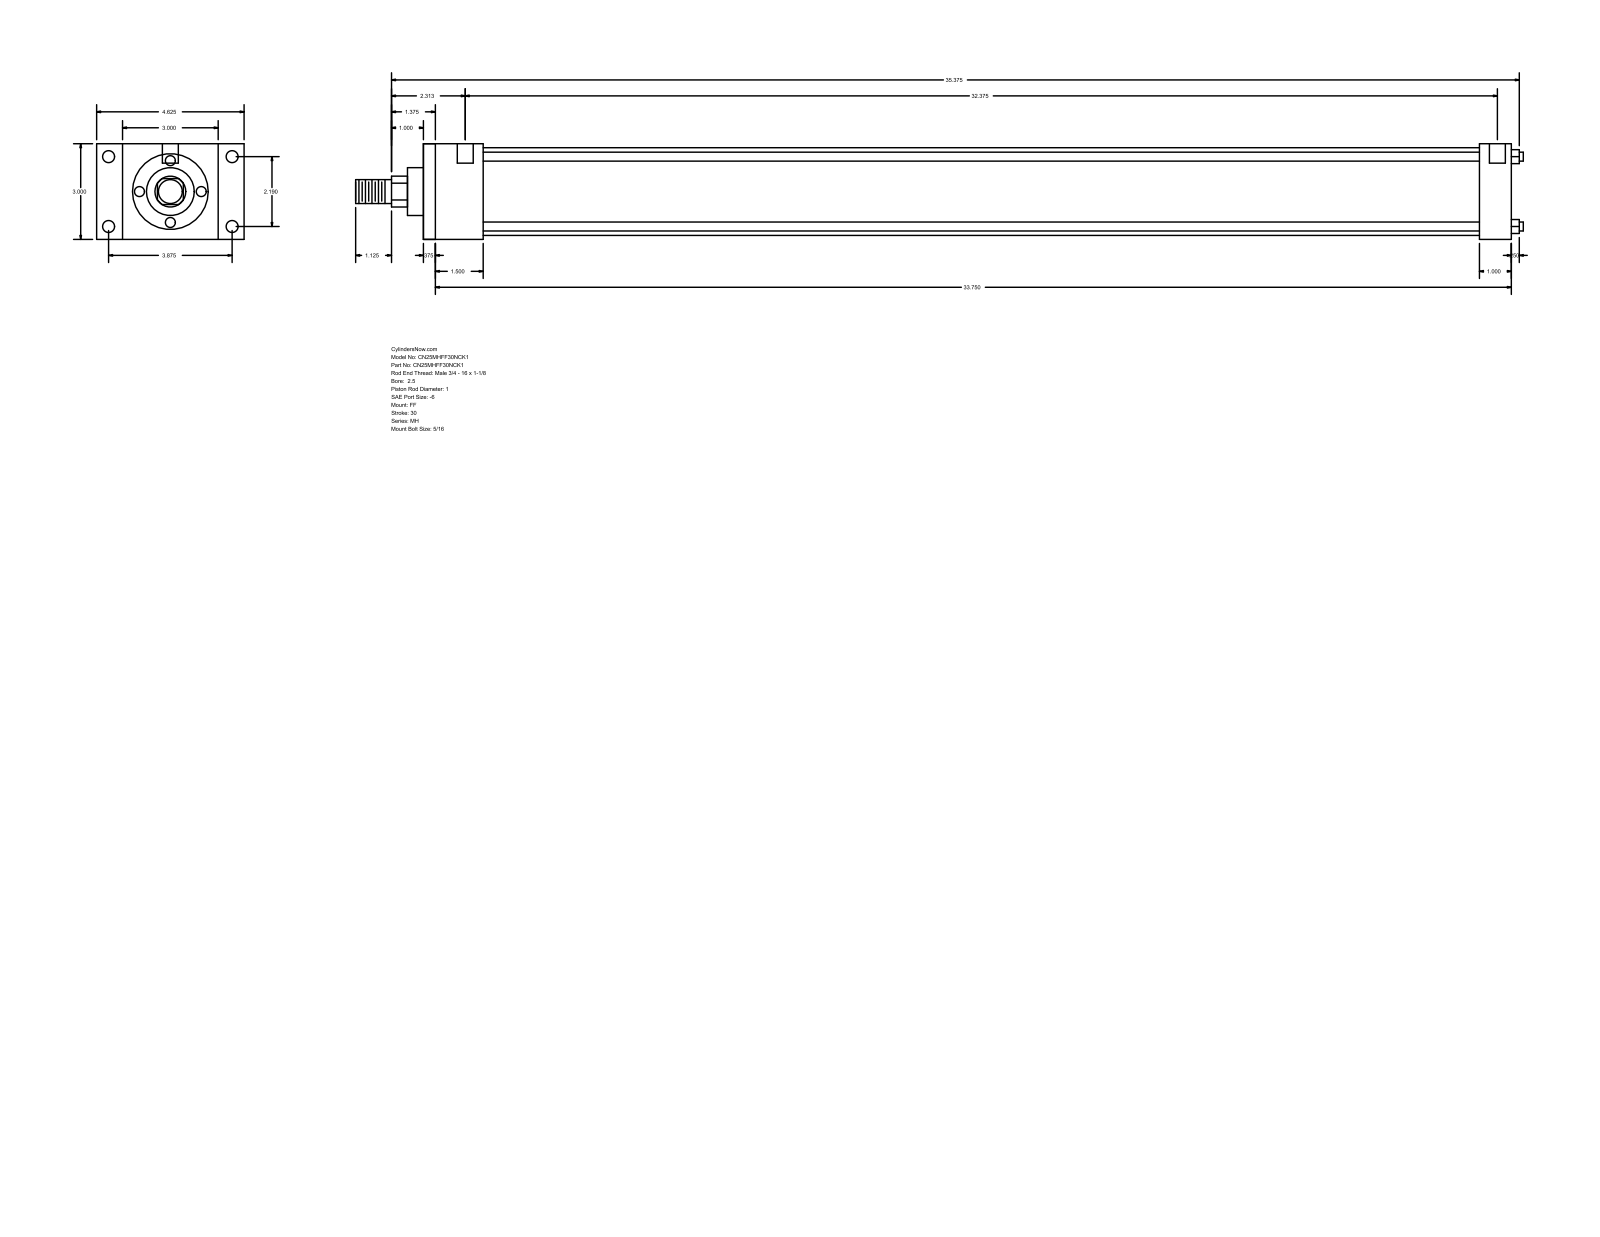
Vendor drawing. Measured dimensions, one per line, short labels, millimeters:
name: MH_FF__0250_1
written by: GSSL Pune (CONFIG_CONTROL_DESIGN)
unit: mm
bodies: 0 solids, 92 faces (64 planar, 28 cylindrical, 0 other)
size: 930.27 × 117.47 × 76.2
holes: 4× ⌀5.56, 4× ⌀9.53, 2× ⌀12.7
bosses: 4× ⌀7.14, 1× ⌀69.85, 1× ⌀38.1, 1× ⌀25.4, 1× ⌀19.05
rounds: 1× R12.29
face distances: 76.2, 866.77, 9.52, 857.25, 25.4, 47.63, 841.37, 38.11, 831.85, 793.74
hole spacings: 55.62, 98.42, 113.05, 830.26, 3.18, 4.76, 822.32, 825.5
